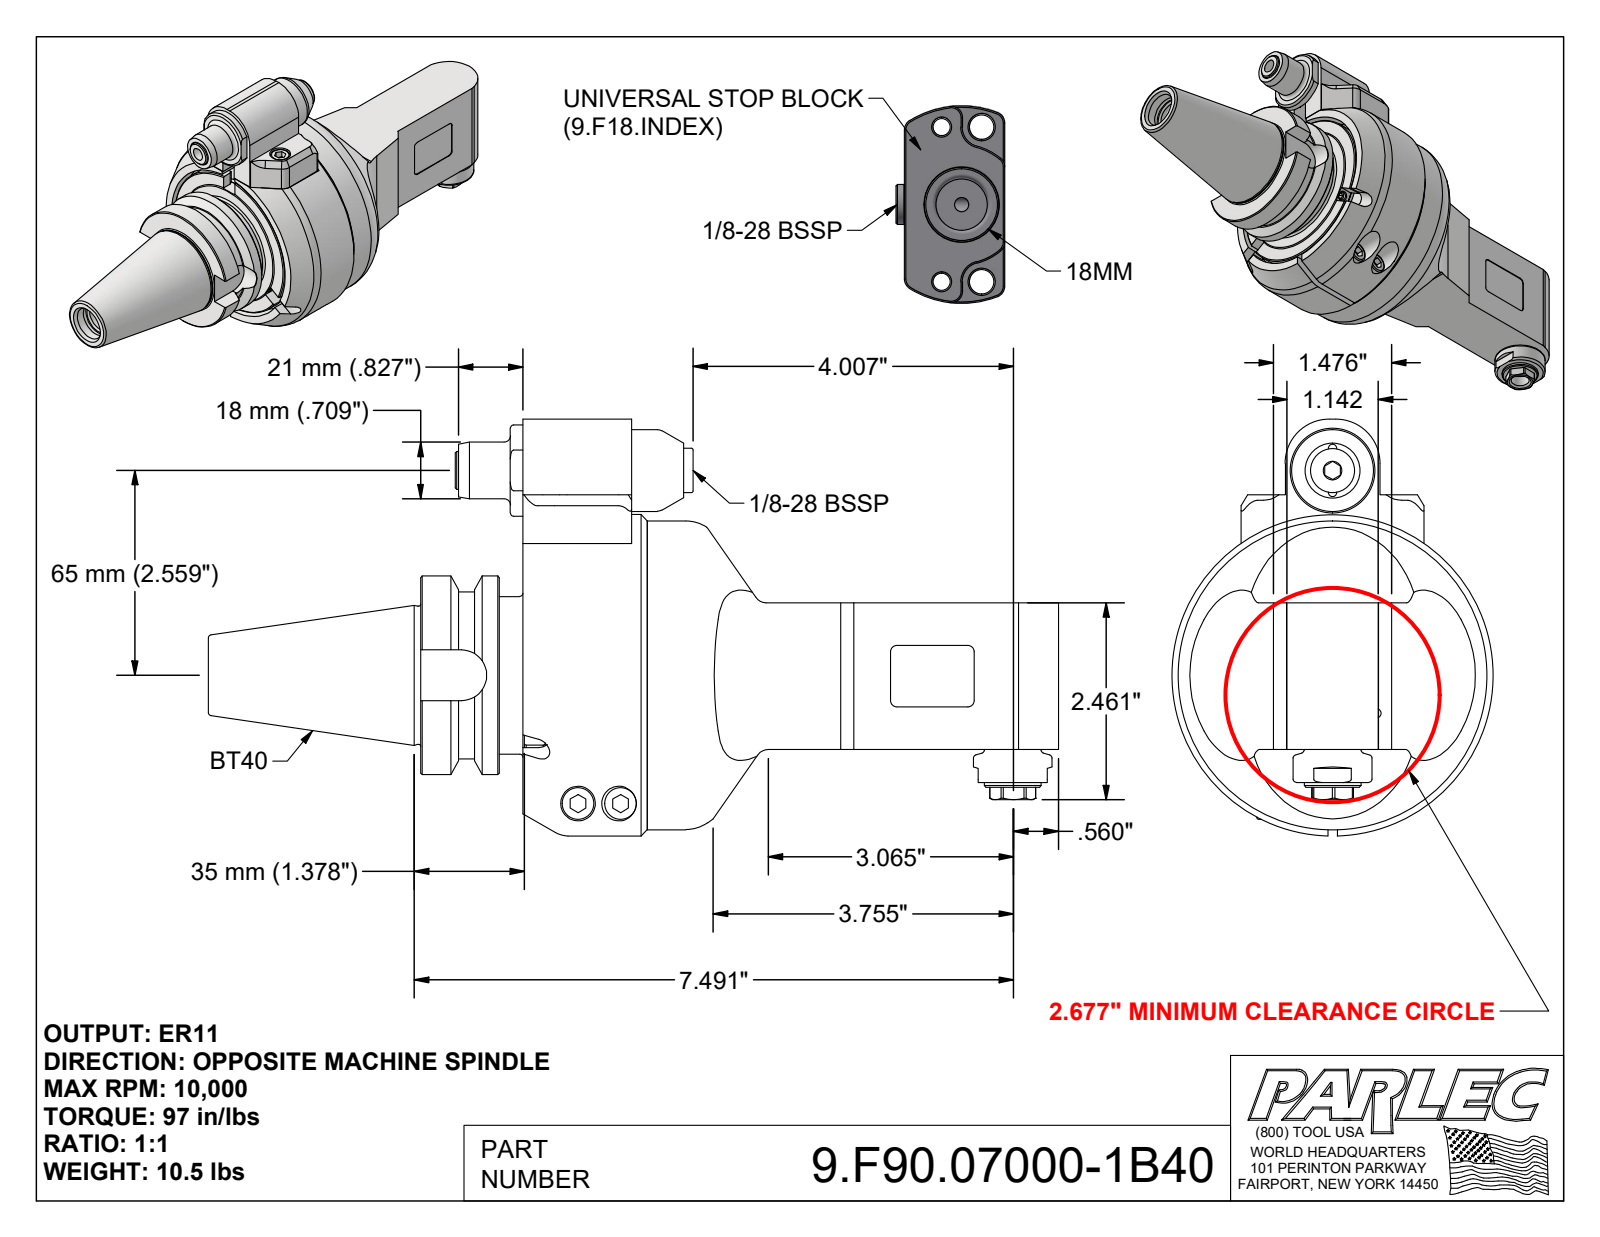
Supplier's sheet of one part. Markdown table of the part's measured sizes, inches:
| quantity | value |
| --- | --- |
| part name | 9.F90.07000-1B40; 9_F90_07000; 9_GA1_346 |
| STEP written by | Autodesk Inventor 2025 (AUTOMOTIVE_DESIGN) |
| units | inches |
| bodies | 5 solids, 486 faces (226 planar, 135 cylindrical, 125 other) |
| overall size | 10.626 × 5.206 × 4.016 |
| volume | 50.16 in³ |
| surface area | 220.5 in² |
| round holes (diameter × count) | 0.335 × 21, 0.102 × 2, 0.165 × 2, 0.197 × 2, 0.409 × 2, 0.433 × 2, 0.098 × 1, 0.118 × 1, 0.256 × 1, 0.276 × 1, 0.295 × 1, 0.354 × 1 |
| round bosses / shafts (diameter × count) | 0.394 × 4, 0.236 × 4, 0.709 × 3, 0.315 × 2, 0.098 × 2, 4.016 × 1, 3.858 × 1, 3.031 × 1 |
| partial cylindrical surfaces (radius × count) | 0.079 × 12, 0.157 × 4, 0.02 × 2, 0.039 × 2, 0.138 × 2, 0.197 × 2, 0.551 × 2, 0.571 × 2 |
| main face-to-face distances | 1.26, 1.555, 0.02, 0.295, 0.738, 0.276, 1.831, 0.315, 2.569, 1.28 |
| hole center spacings | 1.516, 1.824, 0.422, 2.144, 1.47, 2.421, 2.651, 3.002 |
